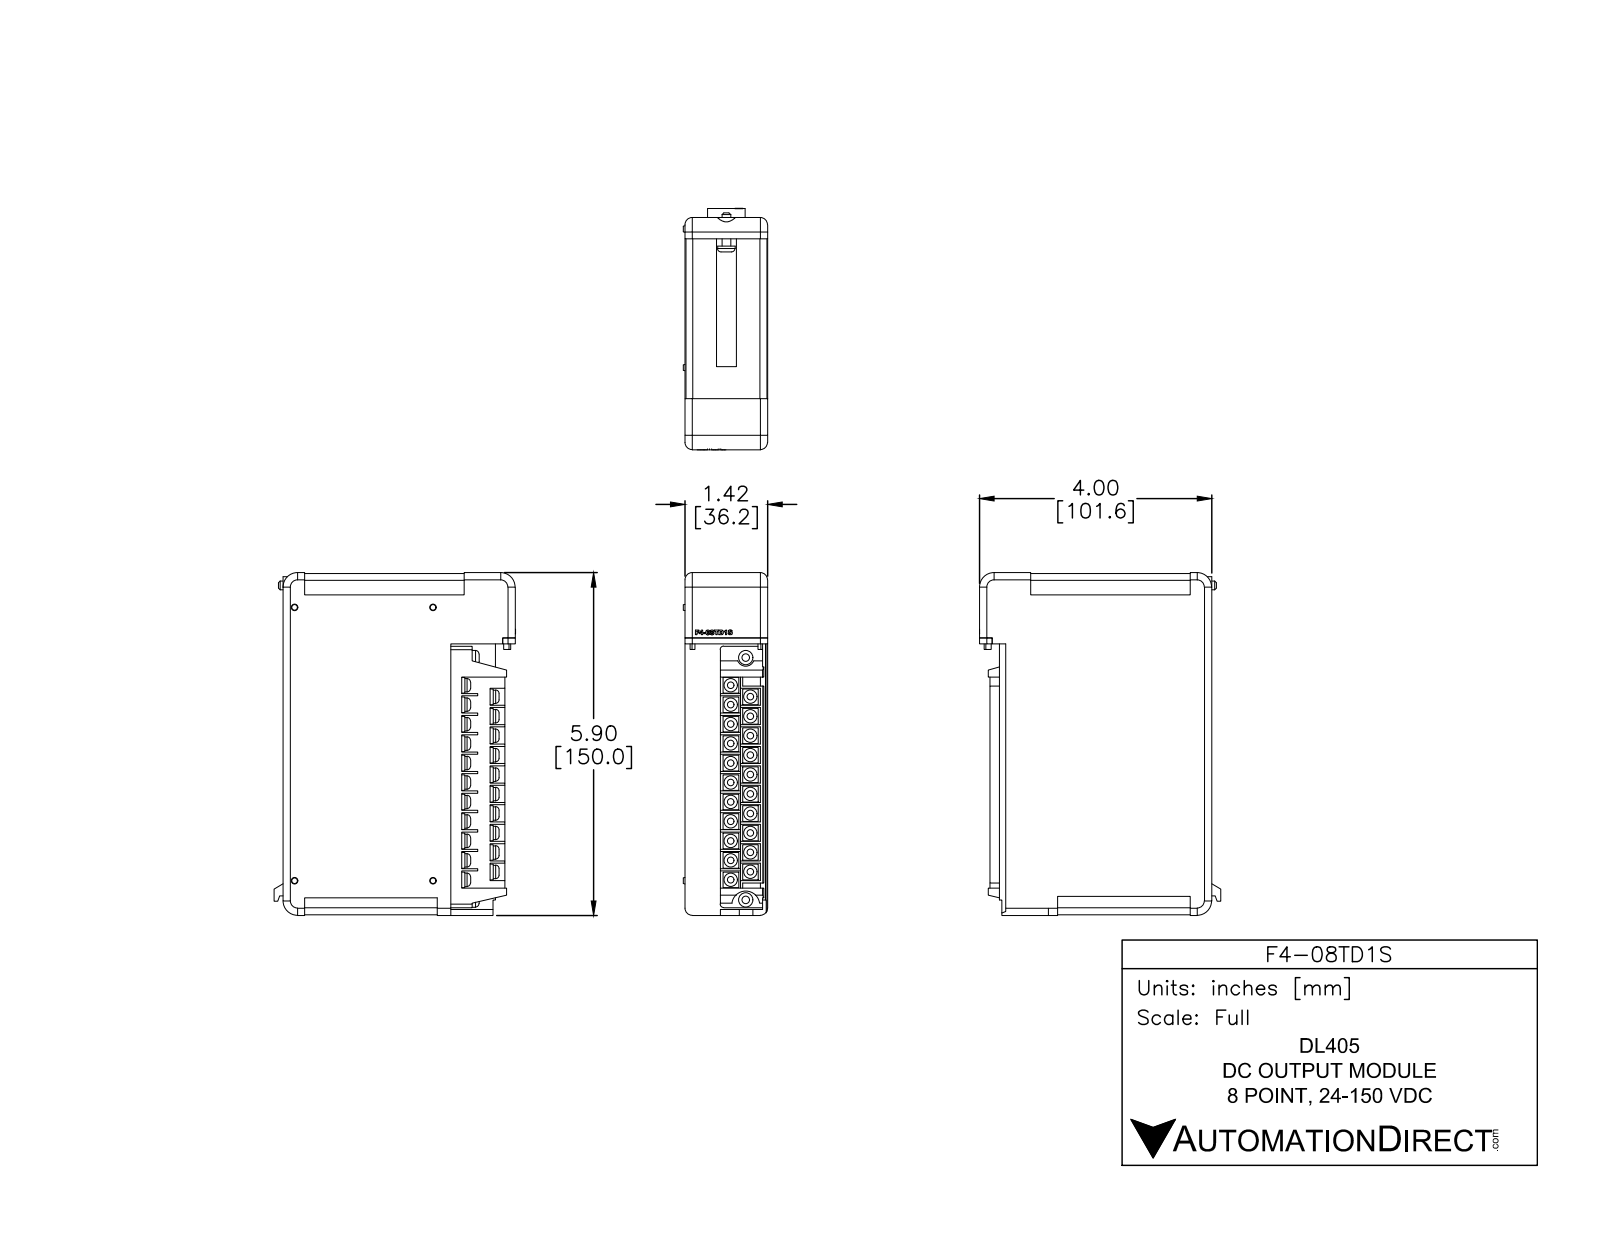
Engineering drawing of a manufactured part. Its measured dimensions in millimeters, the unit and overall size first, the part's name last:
Units: millimetres
Overall size (bounding box): 150 × 105.6 × 37
Round bosses / shafts (diameter × count): ⌀5.8 ×21, ⌀6.4 ×2, ⌀7.6 ×1, ⌀3.8 ×1
Partial cylindrical surfaces — rounded edges, fillets, slot ends (radius × count): R3.2 ×8, R3 ×4, R6.4 ×3, R0.4 ×2, R0.8 ×2, R1.5 ×2, R3.8 ×1, R3.8 ×1
Main face-to-face distances: 36.2, 0.4, 73.4, 149.2, 35.8, 11.9, 5.1, 24.3, 149.6, 30.7
Volume: 450 800 mm³ · Surface area: 56 020 mm²
Bodies: 15 solids, 612 faces (414 planar, 86 cylindrical, 112 other)
Part name (STEP PRODUCT): F4-08TD1S
STEP written by: SolidWorks 2014 (AUTOMOTIVE_DESIGN)
